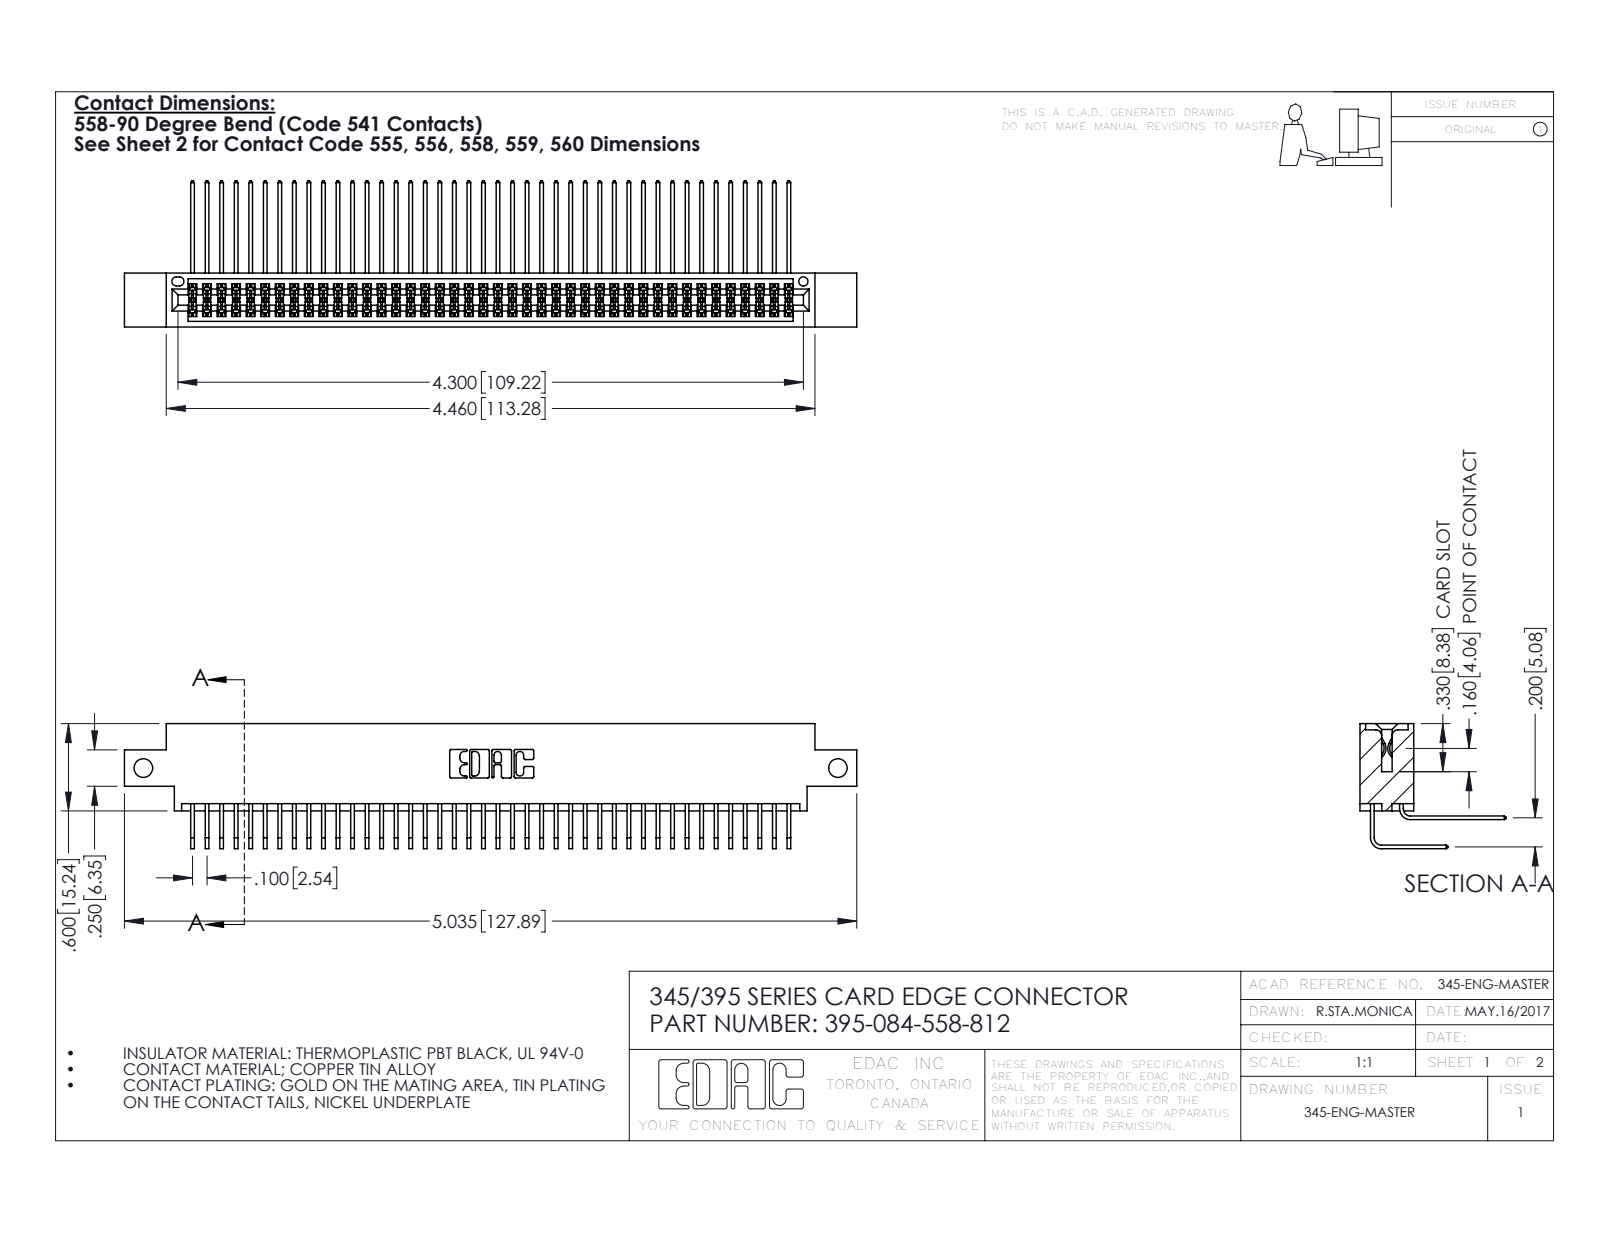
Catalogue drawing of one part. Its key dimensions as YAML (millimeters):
part_name: "345-292-001_558 Tail - 2; 345-292-001_558 559 Tail - 1; 345 Part_0.170 Offset - Side Mount; 395-084-558-812"
step_written_by: "SolidWorks 2016 (CONFIG_CONTROL_DESIGN)"
units: millimeters
bodies: {solids: 85, faces: 4498, planar: 3024, cylindrical: 1474, other: 0}
overall_size: [127.9, 25.5, 21.8]
volume: 12700
surface_area: 21070
round_holes:
  - {diameter: 3.3, count: 2}
  - {diameter: 1.6, count: 1}
partial_cylinders:
  - {radius: 0.2, count: 127}
  - {radius: 0.3, count: 22}
  - {radius: 0.2, count: 6}
  - {radius: 0.8, count: 6}
  - {radius: 0.7, count: 3}
  - {radius: 0.4, count: 2}
  - {radius: 0.5, count: 2}
  - {radius: 0.6, count: 2}
face_to_face_distances: [1.8, 7.6, 5.1, 9.4, 2.5, 6.9, 0.6, 5.7, 4.4, 0.6]
hole_center_spacings: [121.3]
